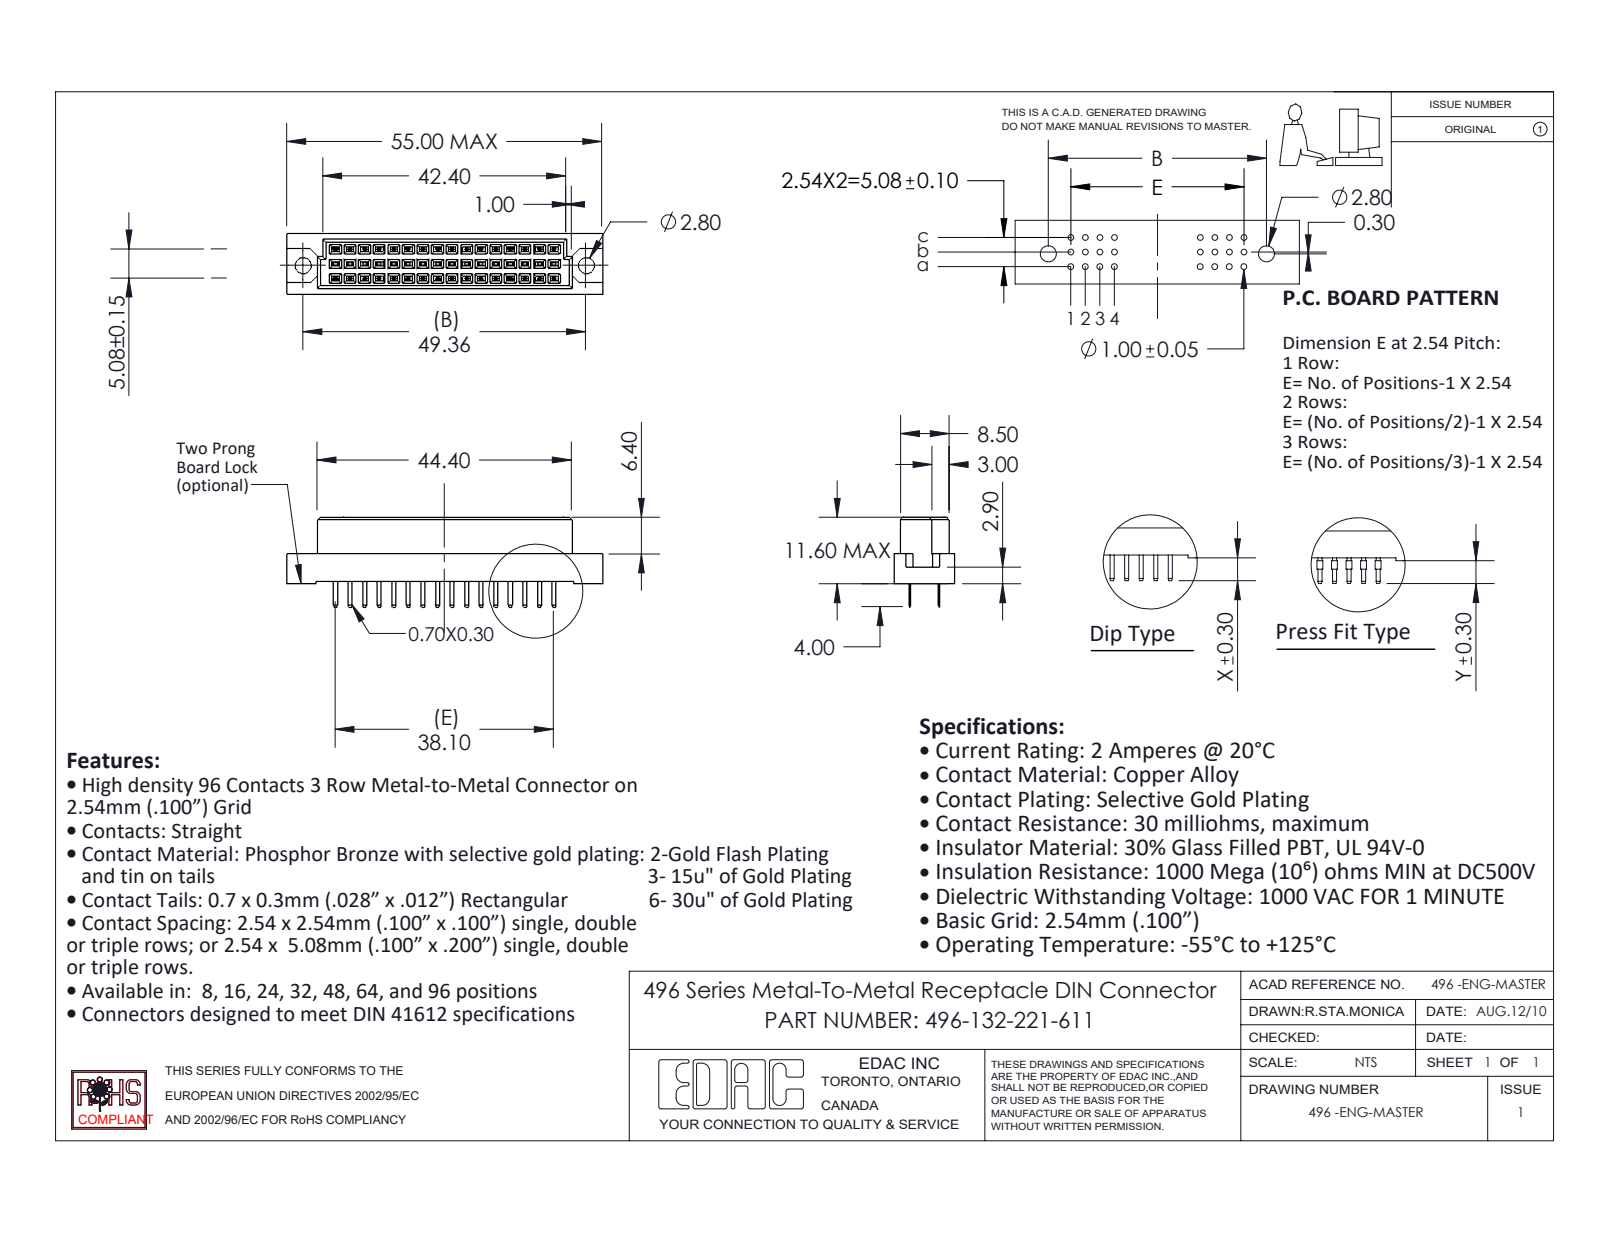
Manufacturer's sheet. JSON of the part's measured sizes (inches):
{"part_name": "496-290_21; 496 Part_48; 496-132-221-611", "step_written_by": "SolidWorks 2020 (CONFIG_CONTROL_DESIGN)", "units": "inches", "bodies": {"solids": 33, "faces": 986, "planar": 982, "cylindrical": 4, "other": 0}, "overall_size": [2.165, 0.614, 0.417], "volume_in3": 0.283, "surface_area_in2": 7.359, "round_holes": [[0.11, 2]], "face_to_face_distances": [0.1, 0.2, 0.041, 0.376, 0.032, 0.022, 0.022, 0.103, 0.115, 0.303], "hole_center_spacings": [1.943]}
